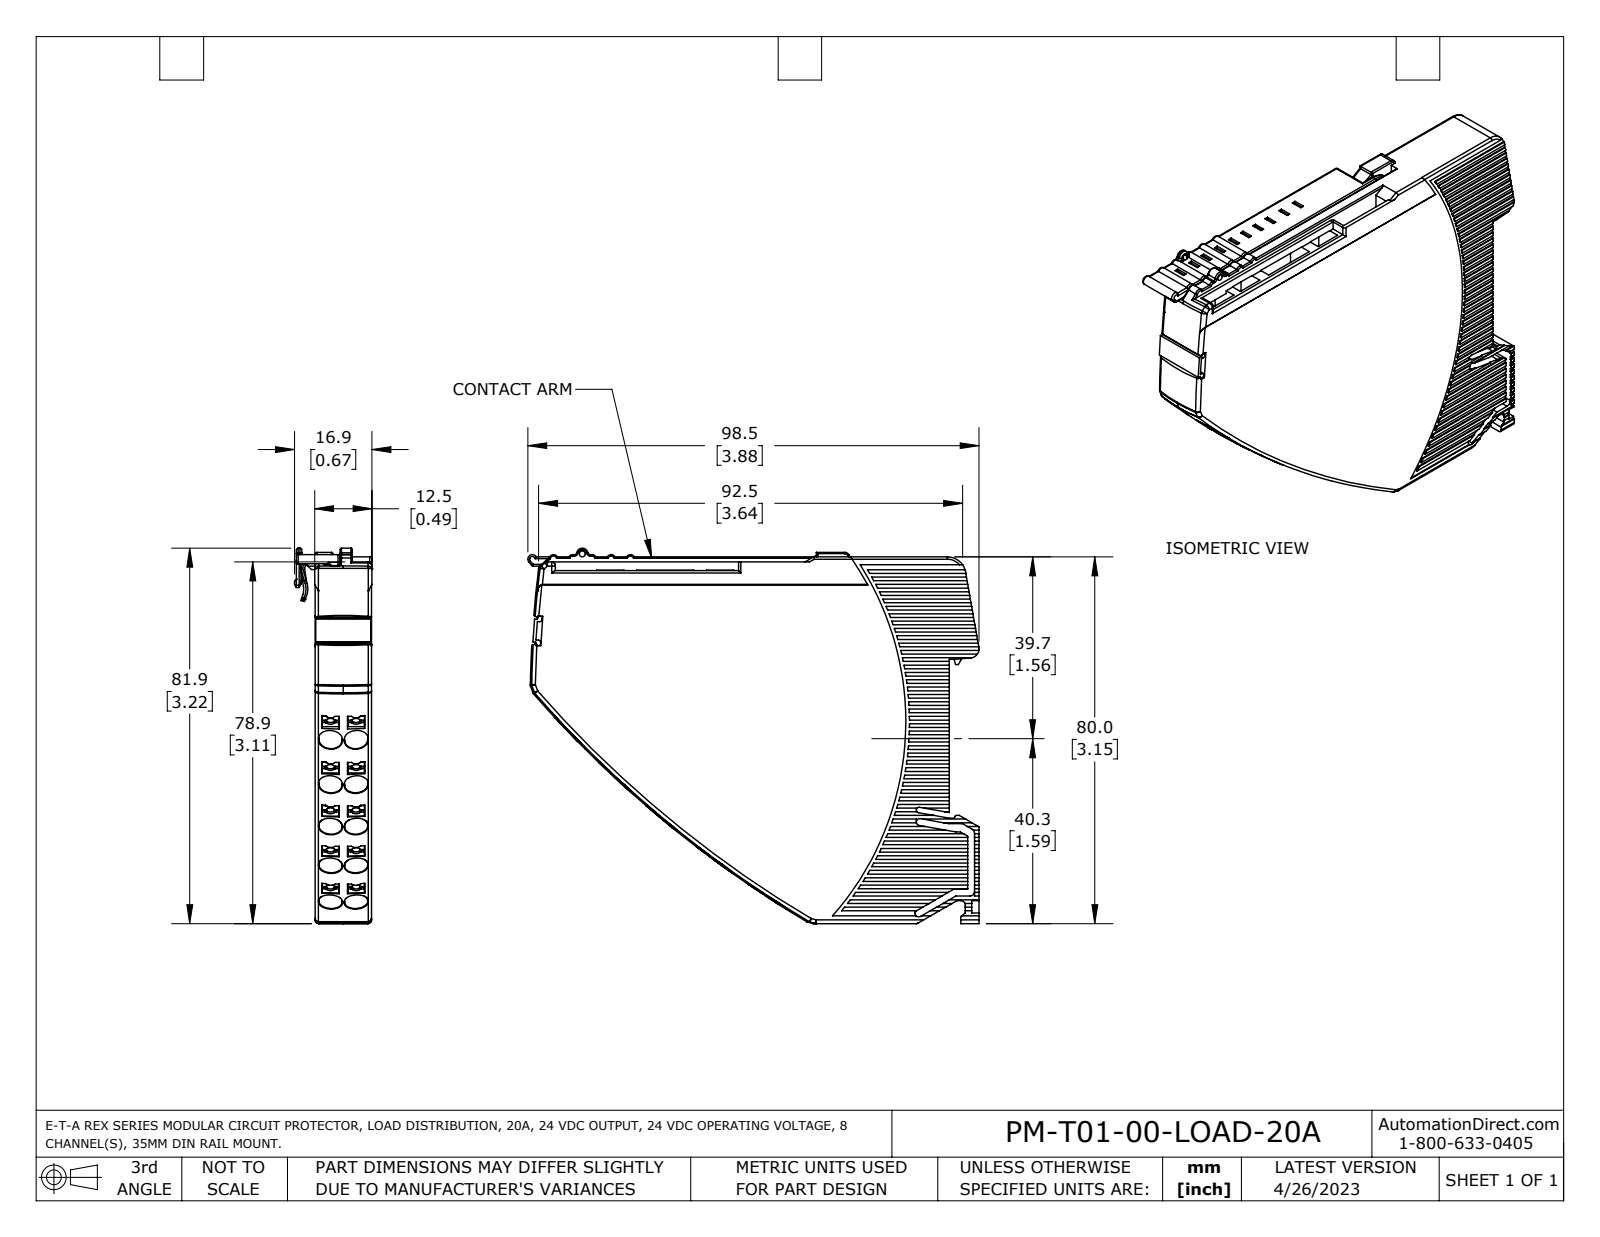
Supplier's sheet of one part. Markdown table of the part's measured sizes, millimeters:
| quantity | value |
| --- | --- |
| part name | t-pm12-t0x-00-load_ik00 |
| STEP written by | SolidWorks 2021 (AUTOMOTIVE_DESIGN) |
| units | millimeters |
| bodies | 2 solids, 1796 faces (1075 planar, 491 cylindrical, 230 other) |
| overall size | 98.5 × 81.9 × 16.9 |
| volume | 69 830 mm³ |
| surface area | 24 930 mm² |
| round holes (diameter × count) | 1.3 × 1, 4.1 × 1 |
| round bosses / shafts (diameter × count) | 4 × 1, 2 × 1 |
| partial cylindrical surfaces (radius × count) | 0.5 × 53, 0.3 × 40, 0.3 × 30, 0.4 × 27, 1 × 26, 2.5 × 20, 0.8 × 13, 0.2 × 10 |
| main face-to-face distances | 12.3, 12.1, 1.5, 5.2, 6.7, 3.7, 10.6, 11.9, 4, 1.5 |
| hole center spacings | 51.4 |
